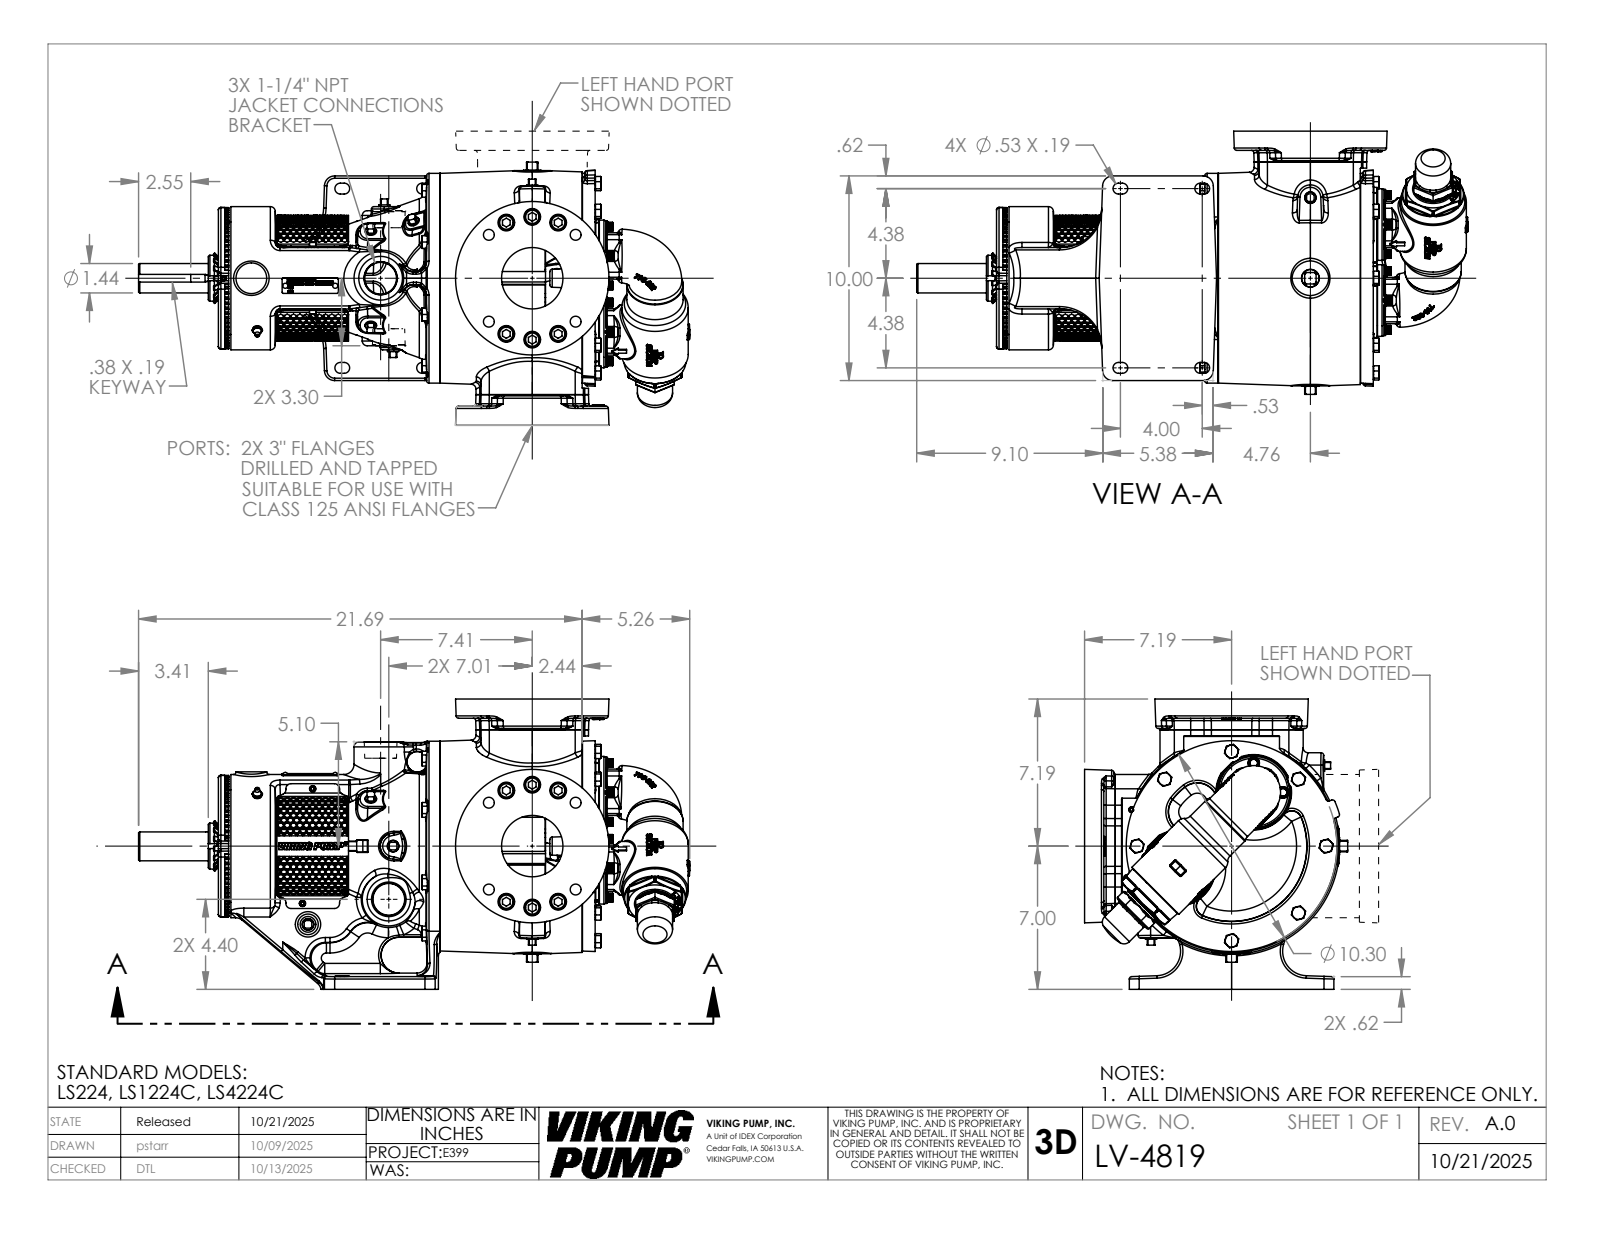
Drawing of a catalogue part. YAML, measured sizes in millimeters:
part_name: "LV-4819"
step_written_by: "SolidWorks 2024 (AUTOMOTIVE_DESIGN)"
units: millimeters
bodies: {solids: 1, faces: 6542, planar: 2037, cylindrical: 1162, other: 3343}
overall_size: [684.39, 360.36, 326.71]
volume: 20790000
surface_area: 998318
round_holes:
  - {diameter: 20.62, count: 12}
  - {diameter: 6.35, count: 9}
  - {diameter: 13.49, count: 8}
  - {diameter: 27.79, count: 8}
  - {diameter: 5.05, count: 6}
  - {diameter: 4.04, count: 3}
  - {diameter: 6.76, count: 2}
  - {diameter: 7.94, count: 2}
  - {diameter: 76.2, count: 2}
  - {diameter: 11.51, count: 1}
  - {diameter: 38.25, count: 1}
  - {diameter: 39.42, count: 1}
round_bosses_or_shafts:
  - {diameter: 19.05, count: 12}
  - {diameter: 15.88, count: 10}
  - {diameter: 14.29, count: 8}
  - {diameter: 15.87, count: 6}
  - {diameter: 88.9, count: 3}
  - {diameter: 7.92, count: 3}
  - {diameter: 4.83, count: 3}
  - {diameter: 260.35, count: 1}
partial_cylinders:
  - {radius: 1.61, count: 109}
  - {radius: 1.75, count: 74}
  - {radius: 3.05, count: 66}
  - {radius: 0.25, count: 56}
  - {radius: 0.76, count: 38}
  - {radius: 12.7, count: 28}
  - {radius: 6.1, count: 16}
  - {radius: 11.43, count: 16}
face_to_face_distances: [360.36, 57.15, 308.06, 12.7, 89.94, 398, 69.85, 35.1, 54.33, 144.27]
hole_center_spacings: [76.2, 107.76, 152.4, 34.93, 26.47, 32.98, 55.37, 58.32]
